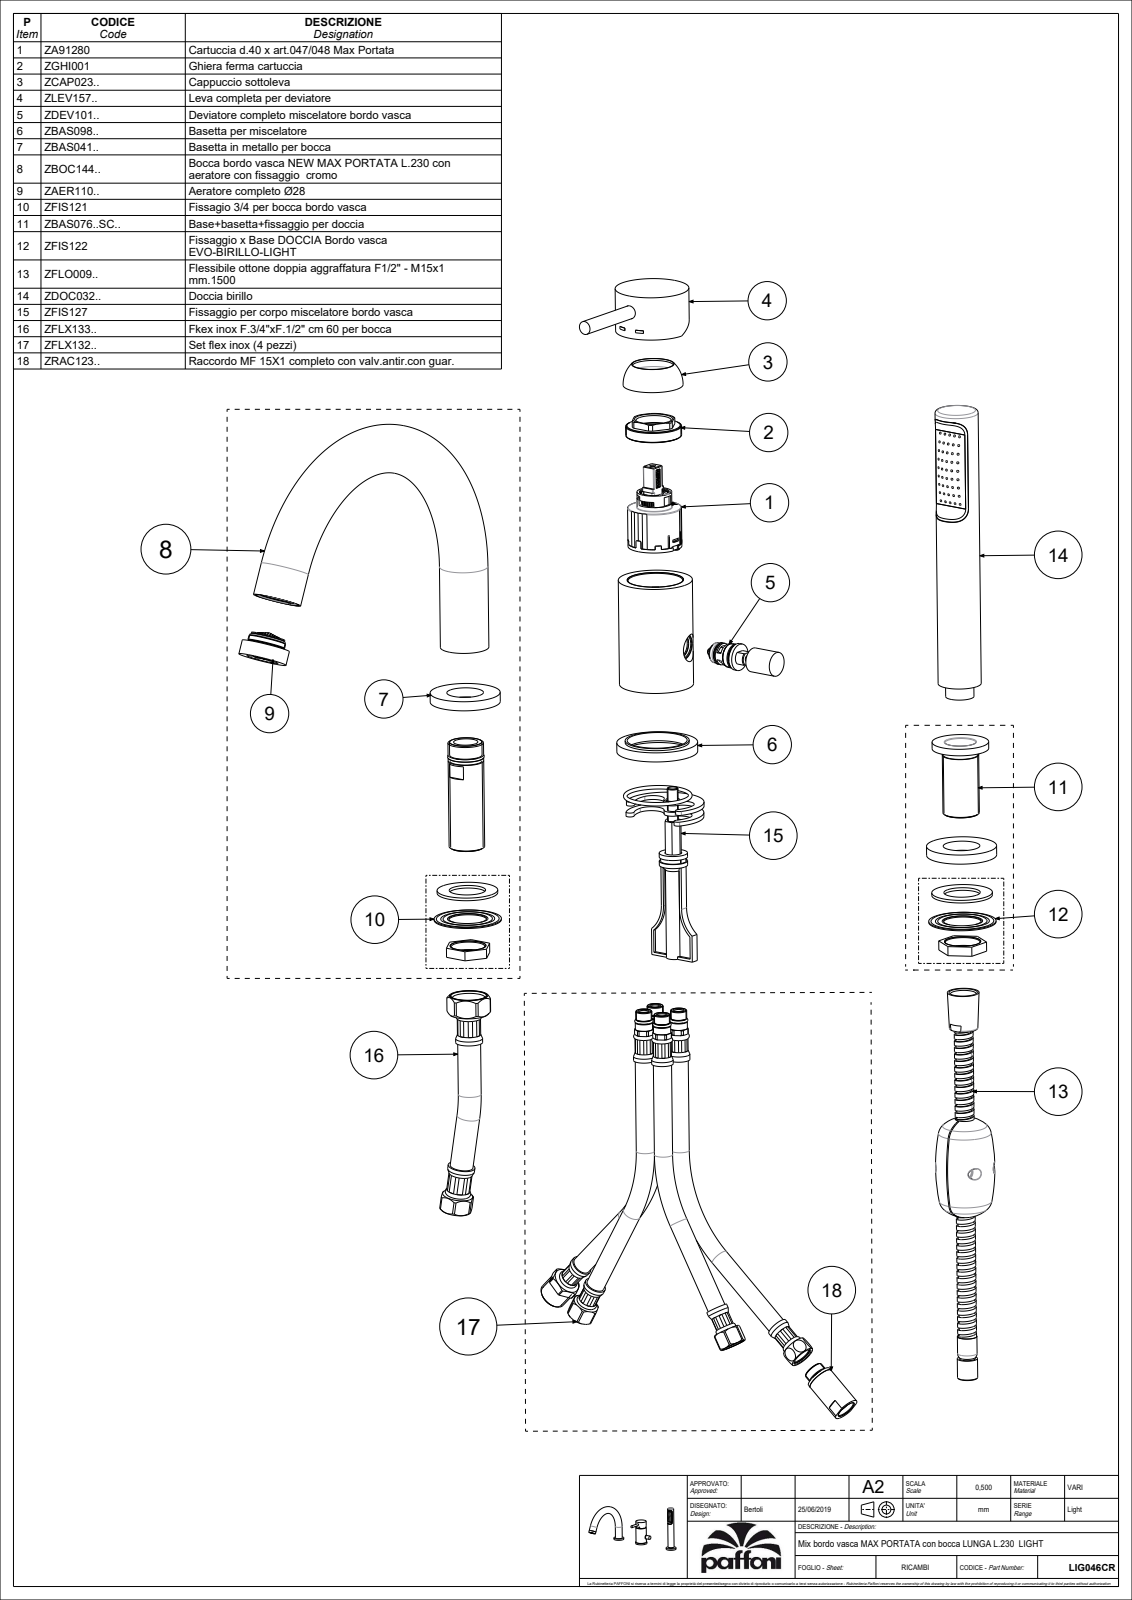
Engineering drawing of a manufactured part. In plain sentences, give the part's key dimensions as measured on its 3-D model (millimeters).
The part is named "LIG046CR". Its 3-D file was written by "CREO PARAMETRIC BY PTC INC, 2022124 (CONFIG_CONTROL_DESIGN)". It is 5 solids with 2312 faces: 1319 planar, 667 cylindrical and 326 other. Overall it measures 402 by 276.71 by 265 millimeters. Its volume is 369 043 cubic millimeters and its surface area 235 180 square millimeters. Round holes: 61 of diameter 0.5, 45 of diameter 1.5, 4 of diameter 8, 4 of diameter 11, 4 of diameter 13, 2 of diameter 3.3, 2 of diameter 5, 2 of diameter 9.8, 2 of diameter 10, 2 of diameter 27.2, 2 of diameter 33, 2 of diameter 34. Round bosses or shafts: 2 of diameter 52, 2 of diameter 44.2, 2 of diameter 36, 2 of diameter 33.9, 2 of diameter 20, 2 of diameter 5, 1 of diameter 60, 1 of diameter 55. Partial cylindrical surfaces (rounded edges, fillets, slot ends): 39 of radius 0.25, 21 of radius 0.5, 12 of radius 0.15, 12 of radius 0.2, 11 of radius 1.5, 10 of radius 1.1, 8 of radius 2, 6 of radius 0.3. The main face-to-face distances are 7, 2, 5, 10, 3, 114.8, 107.8, 59.3, 12, 9. The hole center spacings are 7.91, 13.76, 20.01, 6.5, 3.82, 5.73, 13, 26.39.
